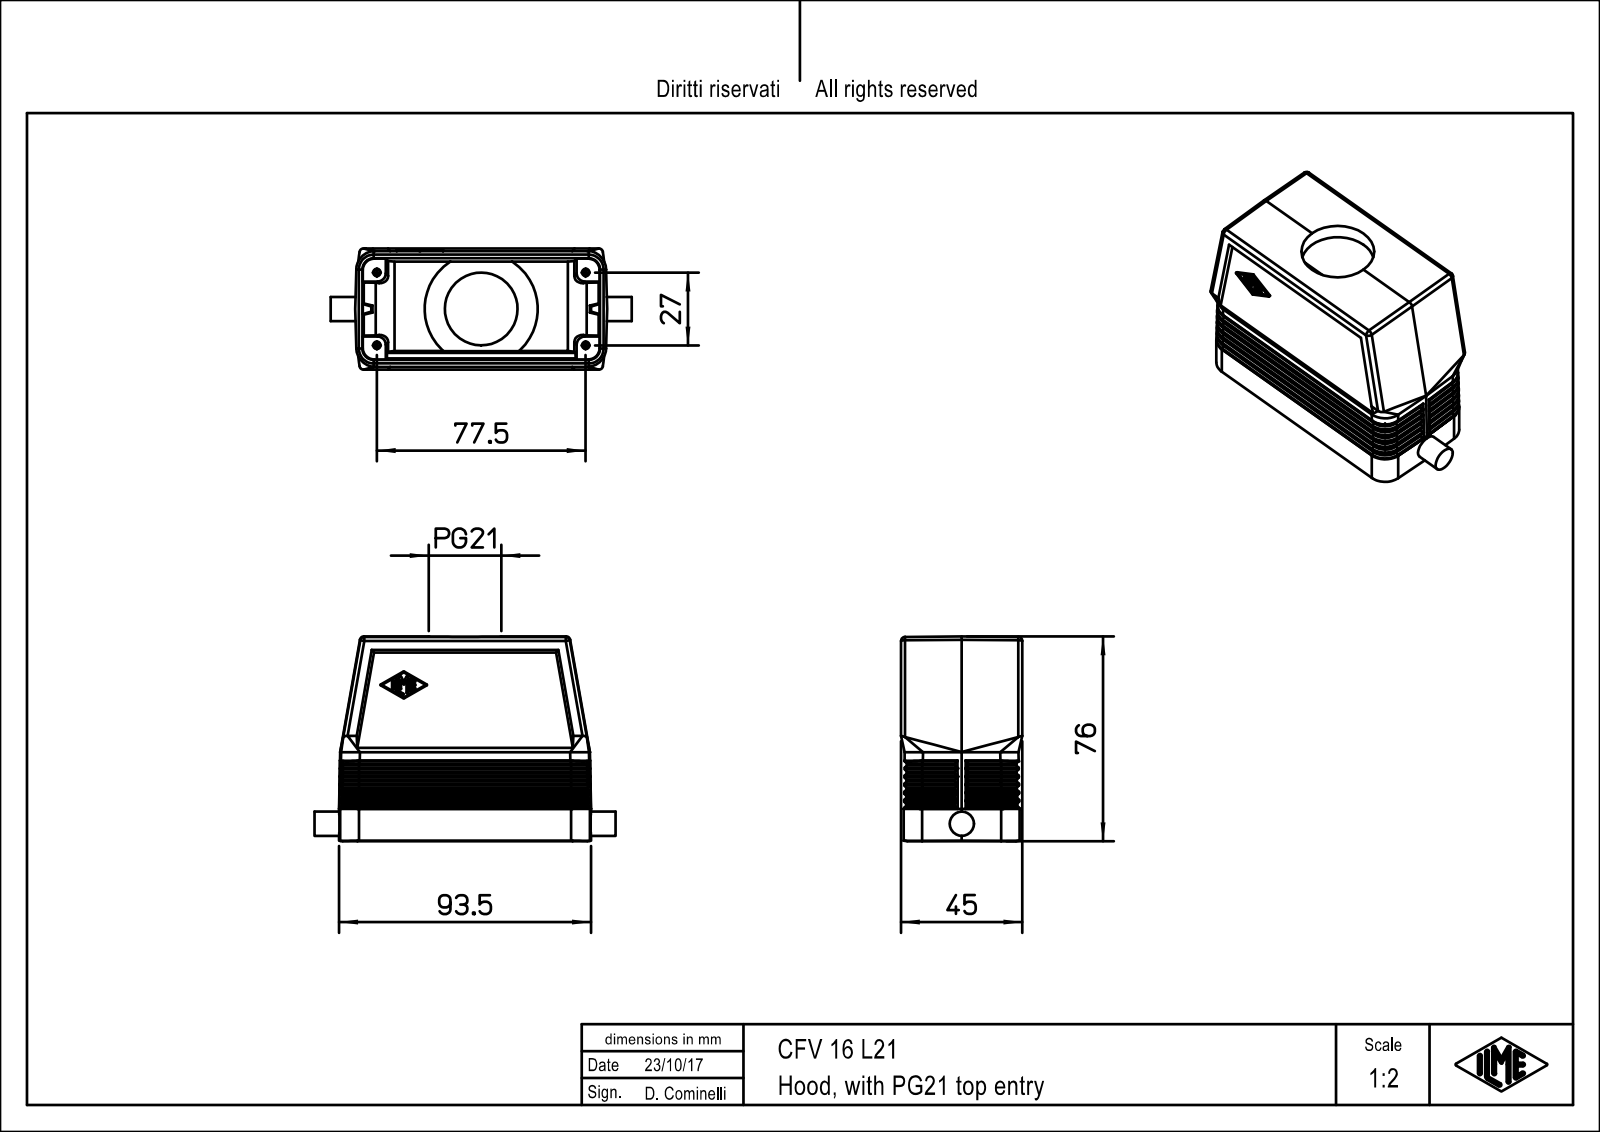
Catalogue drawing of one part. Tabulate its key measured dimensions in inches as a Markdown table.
| quantity | value |
| --- | --- |
| part name | CFV_16_L21 |
| STEP written by | PTC Creo Elements/Direct Modeling 19.0E 27-Jun-2016 (C) Parametric Technology GmbH (AUTOMOTIVE_DESIGN) |
| units | inches |
| bodies | 1 solid, 511 faces (236 planar, 139 cylindrical, 136 other) |
| overall size | 4.398 × 2.992 × 1.772 |
| volume | 5.556 in³ |
| surface area | 68.4 in² |
| round holes (diameter × count) | 1.063 × 1 |
| round bosses / shafts (diameter × count) | 0.354 × 1 |
| partial cylindrical surfaces (radius × count) | 0.02 × 78, 0.013 × 15, 0.059 × 10, 0.276 × 8, 0.118 × 4, 0.165 × 4, 0.007 × 3, 0.026 × 1 |
| main face-to-face distances | 1.693, 0.079, 0.079, 0.335, 0.157, 0.039, 1.732, 0.126, 0.236, 0.237 |
